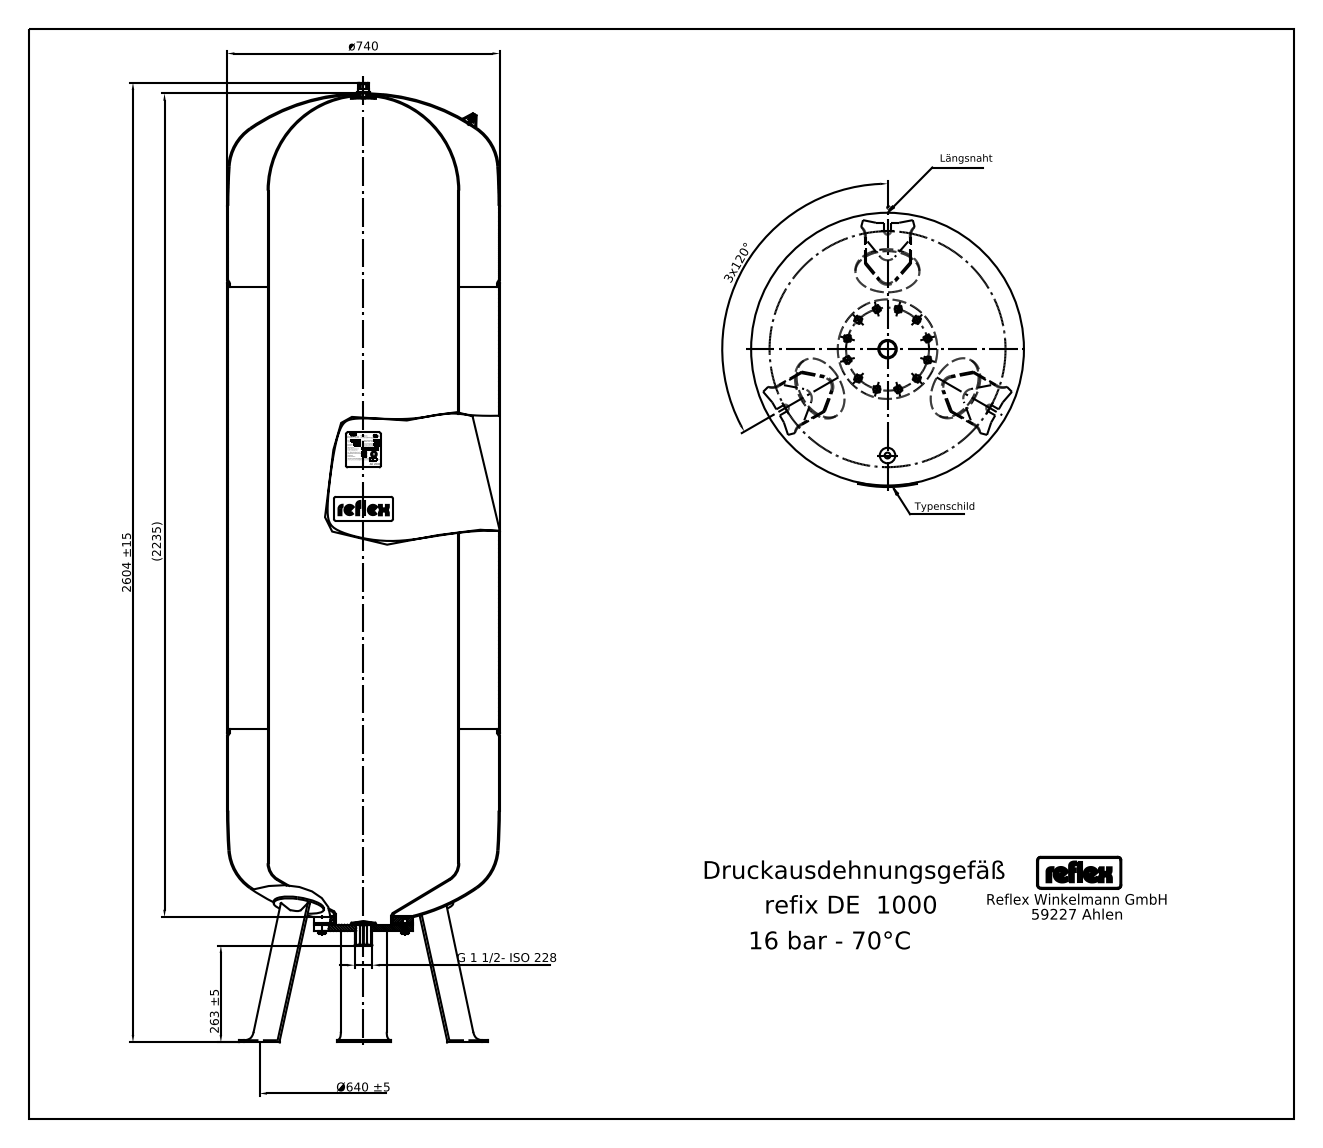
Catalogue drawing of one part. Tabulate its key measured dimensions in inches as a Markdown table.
| quantity | value |
| --- | --- |
| STEP written by | Mechanical Desktop 2008 (CONFIG_CONTROL_DESIGN) |
| units | inches |
| bodies | 20 solids, 441 faces (221 planar, 123 cylindrical, 97 other) |
| overall size | 102.52 × 29.134 × 29.134 |
| volume | 55 880 in³ |
| surface area | 12 720 in² |
| round holes (diameter × count) | 0.555 × 1, 6.299 × 1 |
| round bosses / shafts (diameter × count) | 0.63 × 13, 29.134 × 1, 10.63 × 1, 1.902 × 1, 1.339 × 1, 0.673 × 1, 0.354 × 1, 0.236 × 1 |
| partial cylindrical surfaces (radius × count) | 0.984 × 18, 0.221 × 4, 0.089 × 3, 0.354 × 3, 0.151 × 2, 0.266 × 2, 0.365 × 2, 0.37 × 2 |
| main face-to-face distances | 73.701, 0.63, 0.827, 7.677, 81.378, 0.235, 0.232, 8.307, 82.008, 1.457 |
